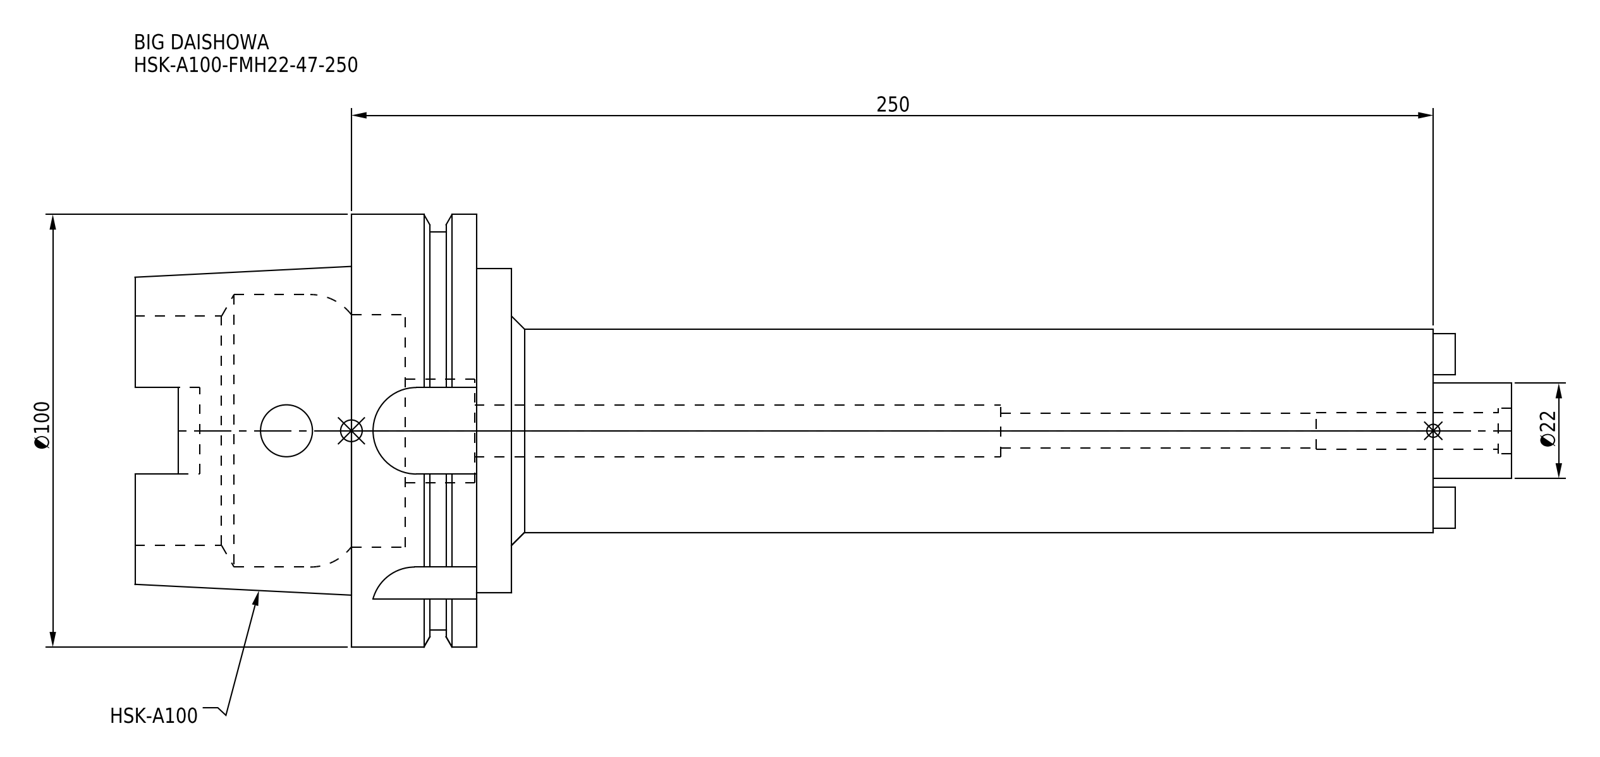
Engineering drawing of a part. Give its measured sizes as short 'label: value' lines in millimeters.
name: HSK-A100-FMH22-47-250
written by: CREO PARAMETRIC BY PTC INC, 2016380 (AUTOMOTIVE_DESIGN)
unit: mm
bodies: 1 solid, 109 faces (47 planar, 46 cylindrical, 16 other)
size: 318 × 100 × 100
volume: 646 816 mm³; area: 92 253 mm²
holes: 2× ⌀12, 1× ⌀8, 1× ⌀8.5, 1× ⌀10.5, 1× ⌀24, 1× ⌀53, 1× ⌀53.8, 1× ⌀63
bosses: 1× ⌀100, 1× ⌀92, 1× ⌀75, 1× ⌀47, 1× ⌀22
rounds: 4× R4.88, 4× R10
face distances: 29, 8, 37, 24.55, 16.55, 12.45, 250, 213, 221, 237.55
